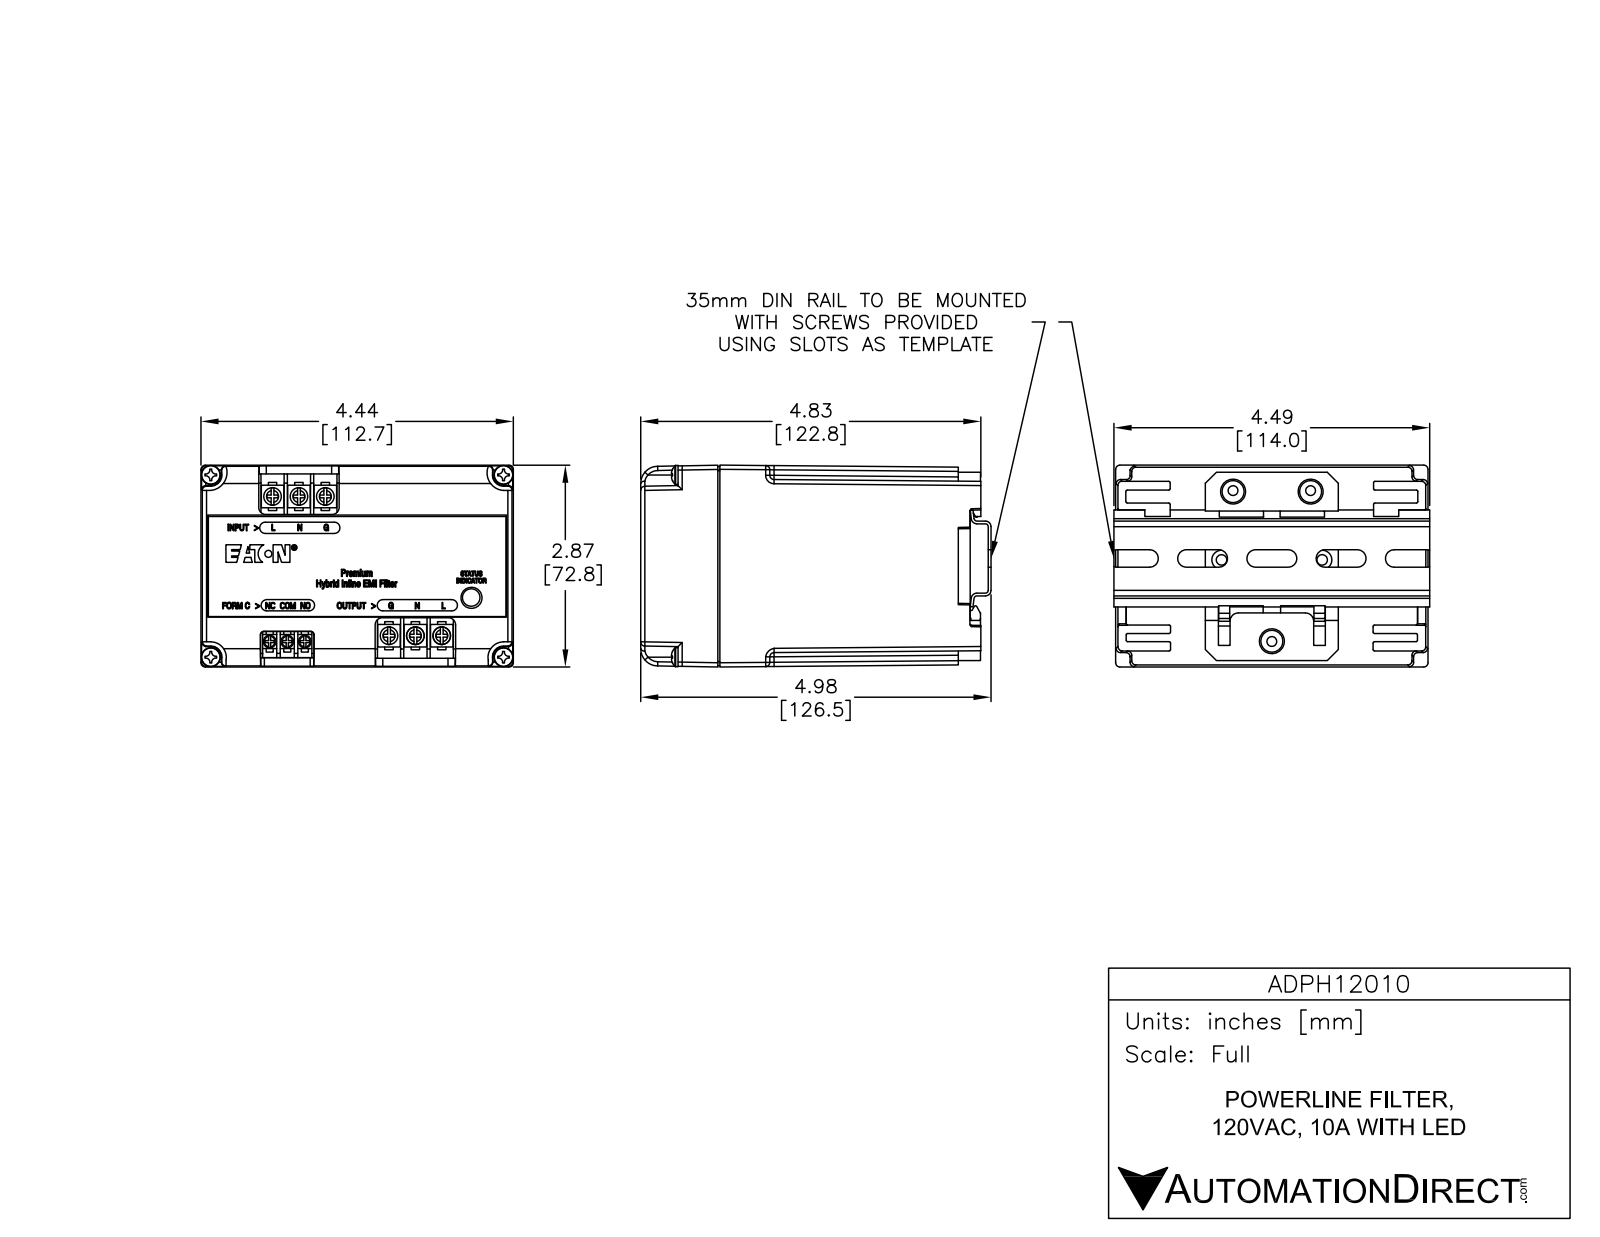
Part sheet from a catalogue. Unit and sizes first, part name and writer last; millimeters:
Units: millimetres
Overall size (bounding box): 125.3 × 114.3 × 72.8
Round holes (diameter × count): ⌀3.9 ×4, ⌀2.5 ×3, ⌀8 ×3, ⌀6.3 ×1
Round bosses / shafts (diameter × count): ⌀6.4 ×6, ⌀1.8 ×6, ⌀6 ×5, ⌀6.6 ×4, ⌀4.6 ×3
Partial cylindrical surfaces — rounded edges, fillets, slot ends (radius × count): R0.6 ×31, R3.1 ×8, R6.4 ×5, R1 ×4, R2 ×4, R3.8 ×4, R1.8 ×3
Main face-to-face distances: 86.1, 114.6, 28.4, 3.8, 10.8, 1, 9.8, 95.9, 124.3, 96.9
Hole centre spacings: 6.4, 56.2, 104.6, 123.6, 12.7, 18.7, 21.5, 21.6
Volume: 922 900 mm³ · Surface area: 114 400 mm²
Bodies: 42 solids, 983 faces (707 planar, 167 cylindrical, 109 other)
Part name (STEP PRODUCT): AD-PH12010
STEP written by: SolidWorks 2013 (AUTOMOTIVE_DESIGN)
